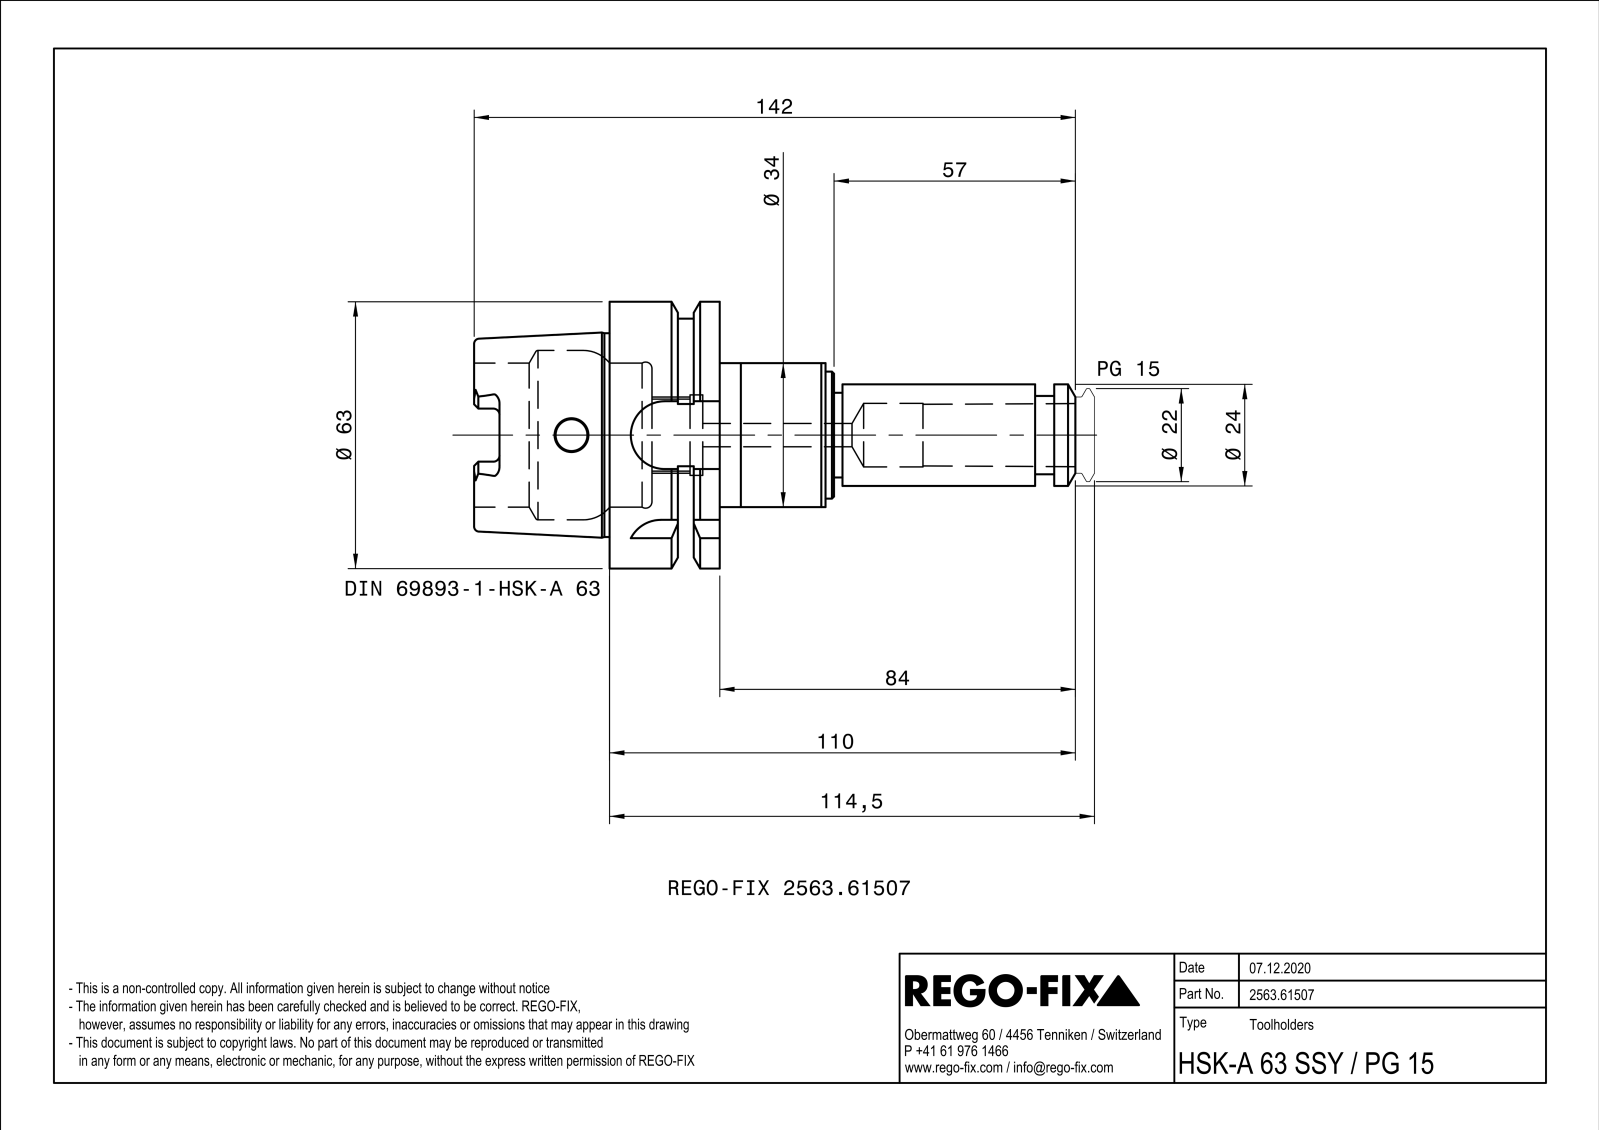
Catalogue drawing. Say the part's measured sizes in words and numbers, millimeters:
The part is named "NOCUT". Its 3-D file was written by "SIEMENS PLM Software Solid Edge ST10 (AUTOMOTIVE_DESIGN)". It is 1 solid with 133 faces: 53 planar, 39 cylindrical and 41 other. Overall it measures 142 by 63 by 63 millimeters. Its volume is 120 714 cubic millimeters and its surface area 33 245 square millimeters. Round holes: 1 of diameter 5.5, 1 of diameter 7.5, 1 of diameter 10, 1 of diameter 15, 1 of diameter 17, 1 of diameter 19, 1 of diameter 24.57, 1 of diameter 34, 1 of diameter 40. Round bosses or shafts: 1 of diameter 63, 1 of diameter 55, 1 of diameter 30, 1 of diameter 26, 1 of diameter 24, 1 of diameter 20, 1 of diameter 19.5. Partial cylindrical surfaces (rounded edges, fillets, slot ends): 6 of radius 1.5, 4 of radius 2.88, 3 of radius 8. The main face-to-face distances are 26, 10, 16, 32, 6.12, 9.88, 22, 58, 42, 31.
